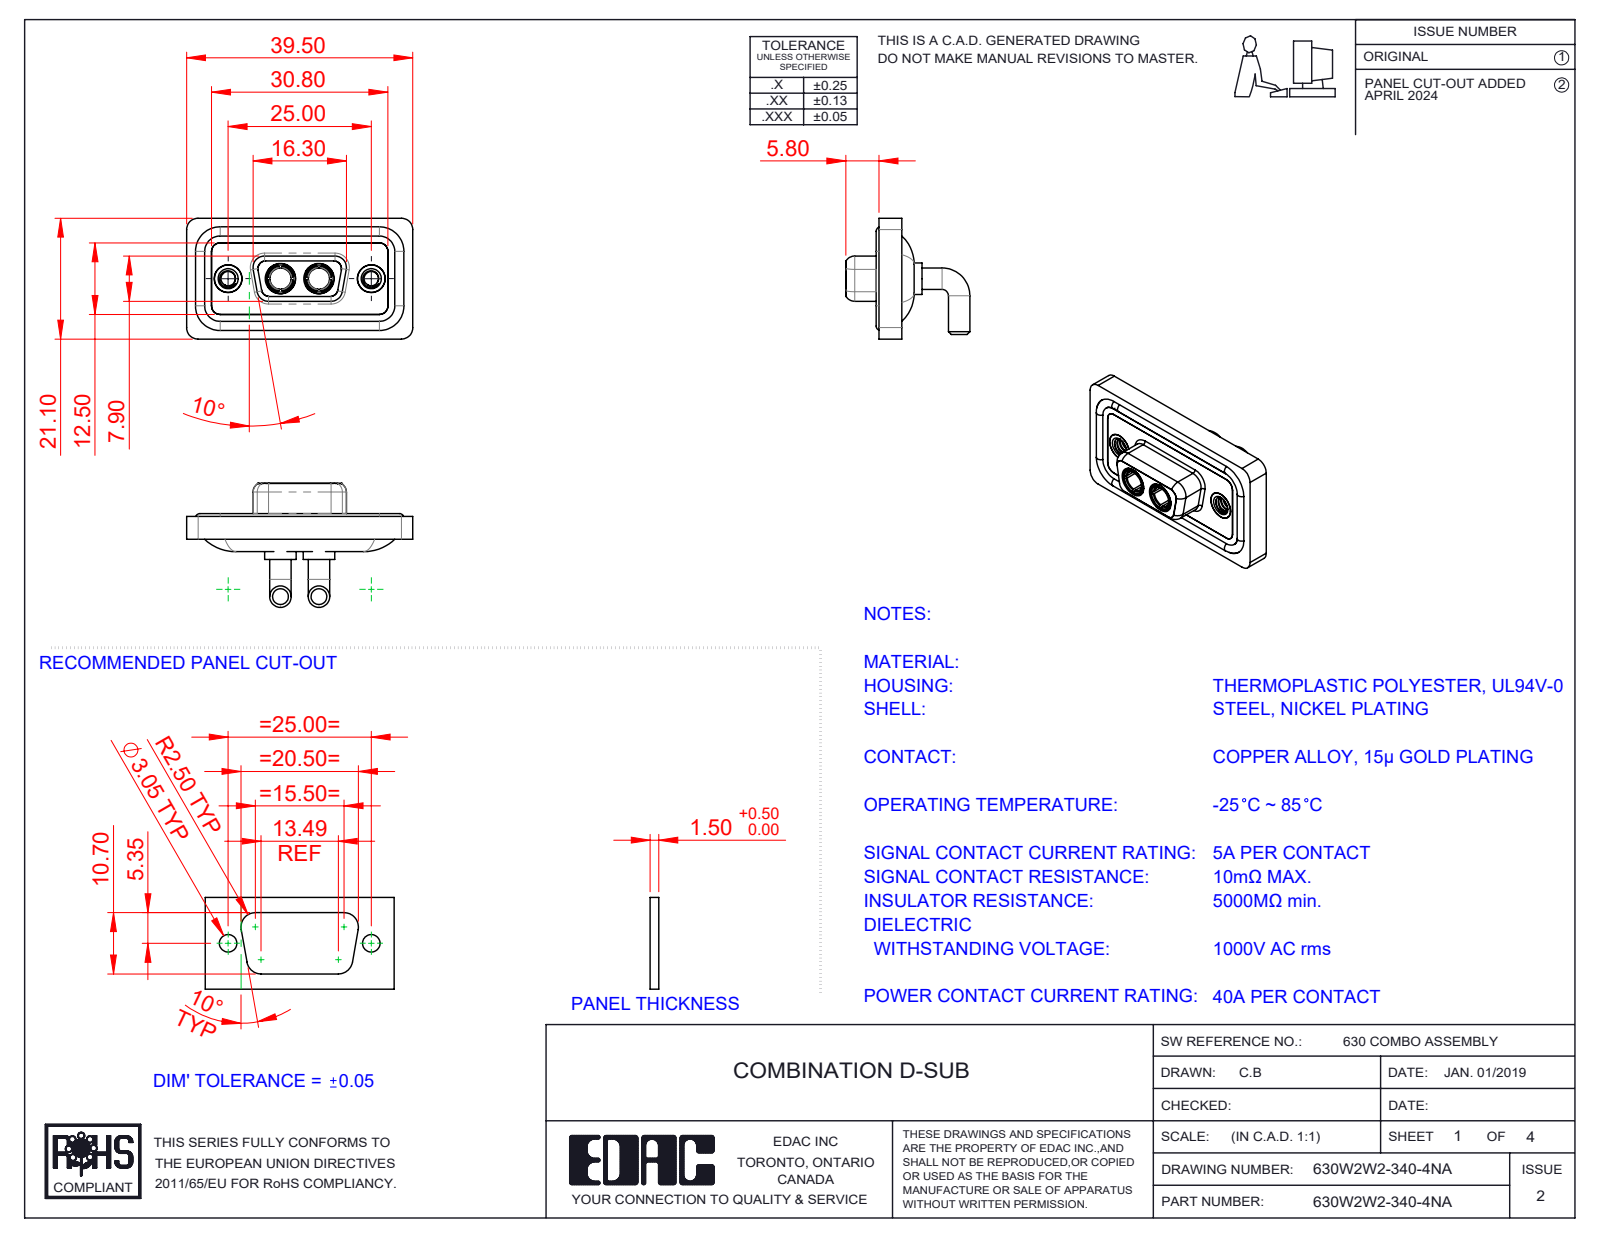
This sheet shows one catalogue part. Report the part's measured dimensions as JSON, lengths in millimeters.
{"part_name": "630Combo Housing_2W2; 630Combo Waterproof Housing_09 Contacts; Power Socket_40A RA; 630W2W2-340-4NA (+3 more)", "step_written_by": "SolidWorks 2023 (CONFIG_CONTROL_DESIGN)", "units": "millimeters", "bodies": {"solids": 11, "faces": 536, "planar": 163, "cylindrical": 236, "other": 137}, "overall_size": [39.5, 21.68, 21.1], "volume_mm3": 4954, "surface_area_mm2": 7876, "round_holes": [[4.85, 4], [2.5, 2], [3.7, 2], [4, 2], [4.05, 2], [5, 2], [5.3, 2]], "round_bosses_or_shafts": [[3.75, 4], [1.6, 4], [5.5, 2], [5.2, 2], [4.96, 2], [4.95, 2], [4.8, 2], [4.75, 2]], "partial_cylinders_radius": [[1.5, 18], [2, 18], [1.35, 8], [1.6, 8], [0.25, 4], [0.5, 4], [0.6, 4], [0.65, 4]], "face_to_face_distances": [0.4, 1.8, 1.1, 2.9, 2.5, 1.6, 3.1, 2.1, 3.7, 1.5], "hole_center_spacings": [9.14, 15.86, 6.72, 25]}
